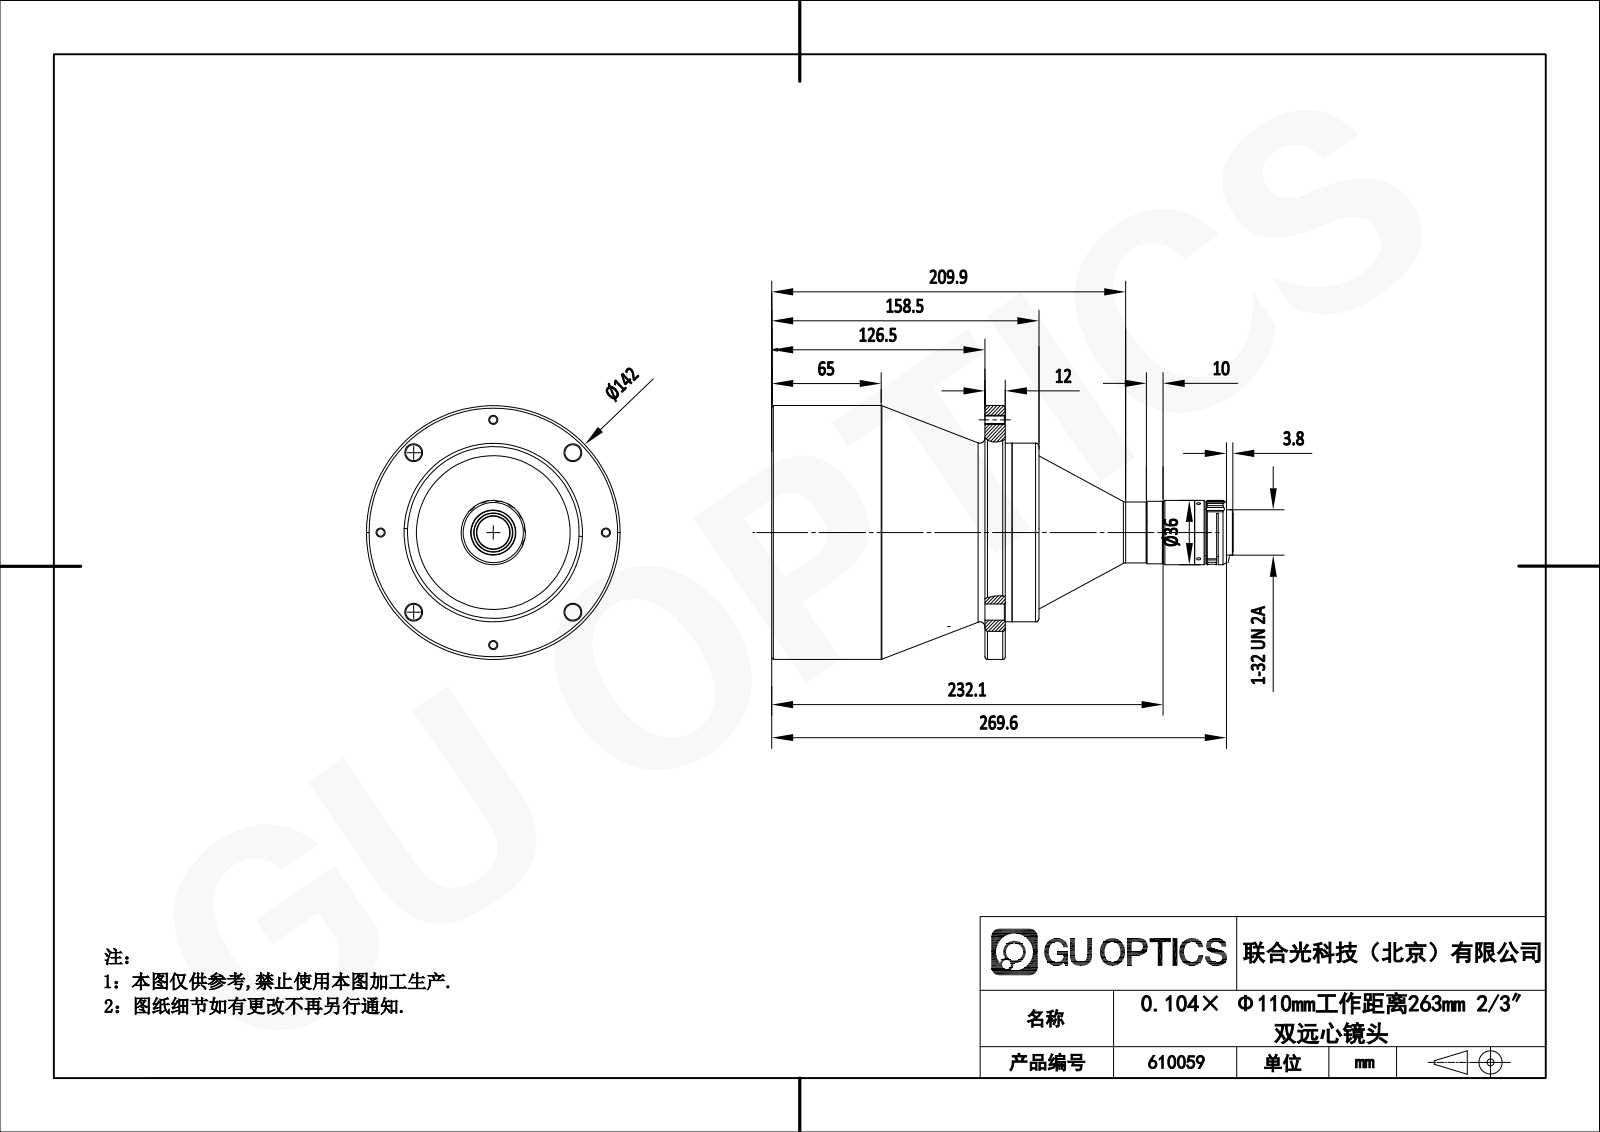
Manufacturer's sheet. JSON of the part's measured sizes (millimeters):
{"part_name": "DTCM230-110-AL", "step_written_by": "SolidWorks 2017 (CONFIG_CONTROL_DESIGN)", "units": "millimeters", "bodies": {"solids": 1, "faces": 183, "planar": 22, "cylindrical": 84, "other": 77}, "overall_size": [273.52, 142, 142], "volume_mm3": 2258000, "surface_area_mm2": 119685, "round_holes": [[4.2, 4], [9, 4], [2.5, 3], [18.5, 1], [22, 1], [86, 1], [133.3, 1]], "round_bosses_or_shafts": [[142, 1], [100, 1], [36, 1], [35, 1], [34, 1], [33.09, 1], [25.4, 1]], "partial_cylinders_radius": [[3, 14], [4, 7], [1.02, 1], [1.4, 1], [2.4, 1]], "face_to_face_distances": [12, 32, 20, 126.5, 138.5, 158.5, 269.62, 143.12, 131.12, 111.12], "hole_center_spacings": [48.22, 63, 89.1, 116.41, 126, 126.01]}
